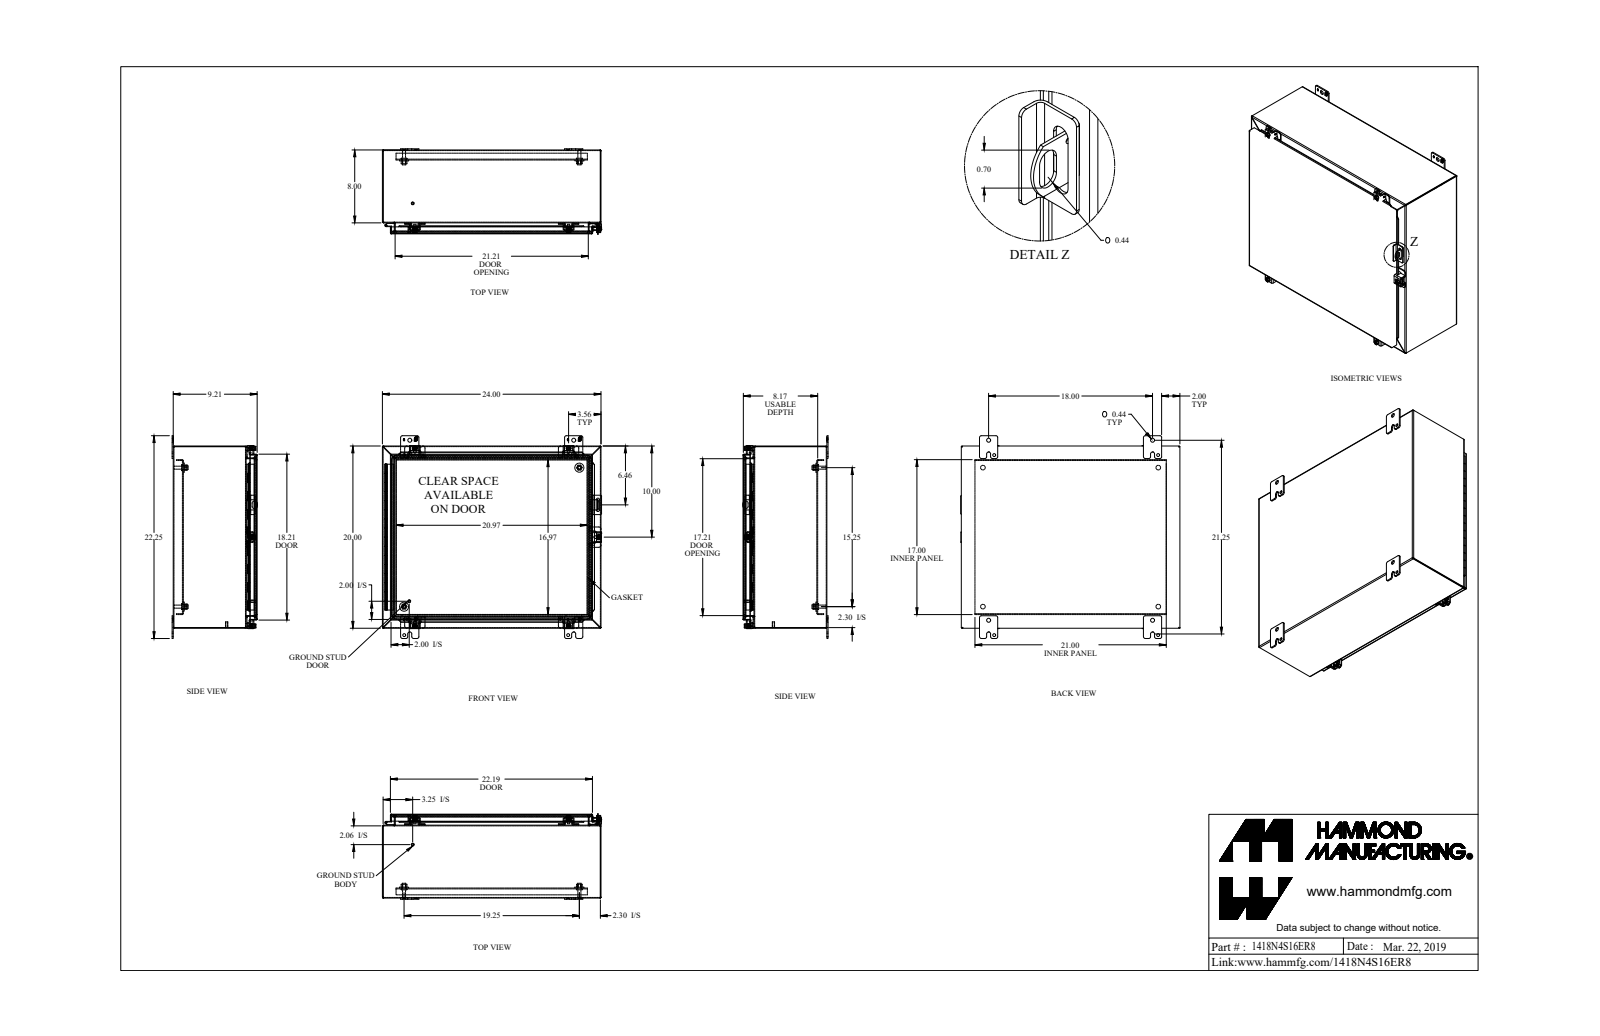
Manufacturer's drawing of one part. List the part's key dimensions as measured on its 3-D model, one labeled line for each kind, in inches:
Part name (STEP PRODUCT): 1418N4S16ER8_Default
STEP written by: SolidWorks 2019 (CONFIG_CONTROL_DESIGN)
Units: inches
Bodies: 43 solids, 1449 faces (792 planar, 517 cylindrical, 140 other)
Overall size (bounding box): 24.063 × 22.25 × 9.375
Volume: 184.2 in³ · Surface area: 4 851 in²
Round holes (diameter × count): ⌀0.213 ×5, ⌀0.375 ×5, ⌀0.265 ×4, ⌀0.313 ×4, ⌀0.437 ×4, ⌀0.5 ×4, ⌀0.307 ×2, ⌀0.445 ×2, ⌀0.11 ×1, ⌀0.125 ×1, ⌀0.265 ×1
Round bosses / shafts (diameter × count): ⌀0.5 ×5, ⌀0.39 ×5, ⌀0.244 ×5, ⌀0.65 ×4, ⌀0.375 ×4, ⌀0.332 ×4, ⌀1 ×2, ⌀0.313 ×2
Partial cylindrical surfaces — rounded edges, fillets, slot ends (radius × count): R0.188 ×26, R0.036 ×24, R0.108 ×24, R0.25 ×24, R0.048 ×21, R0.143 ×21, R0.125 ×12, R0.141 ×10
Main face-to-face distances: 0.072, 9.066, 9.138, 0.072, 9.138, 9.21, 0.095, 0.937, 19.928, 1.009
Hole centre spacings: 2.434, 3.065, 17.416, 18, 18.187, 24.559, 26.722, 15.25
